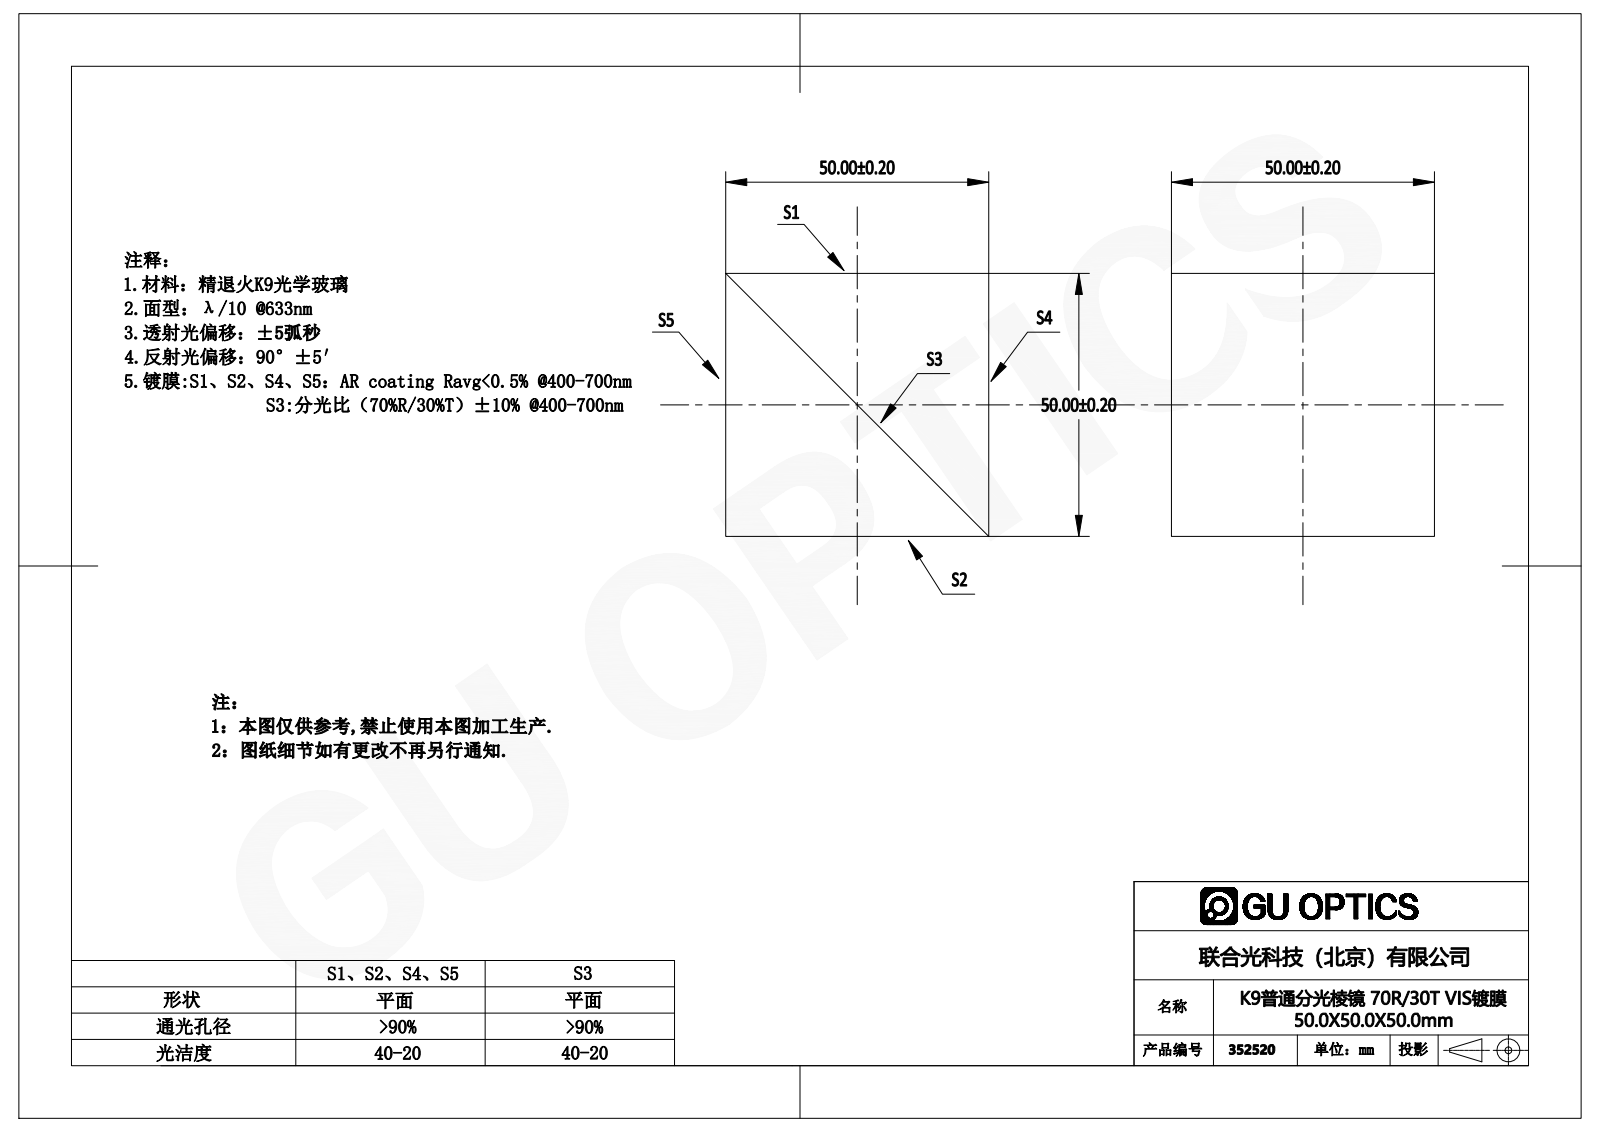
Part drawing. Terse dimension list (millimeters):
name: 352518
written by: SolidWorks 2016 (AUTOMOTIVE_DESIGN)
unit: mm
bodies: 2 solids, 10 faces (10 planar, 0 cylindrical, 0 other)
size: 50 × 50 × 50
volume: 125 000 mm³; area: 22 071 mm²
face distances: 50
